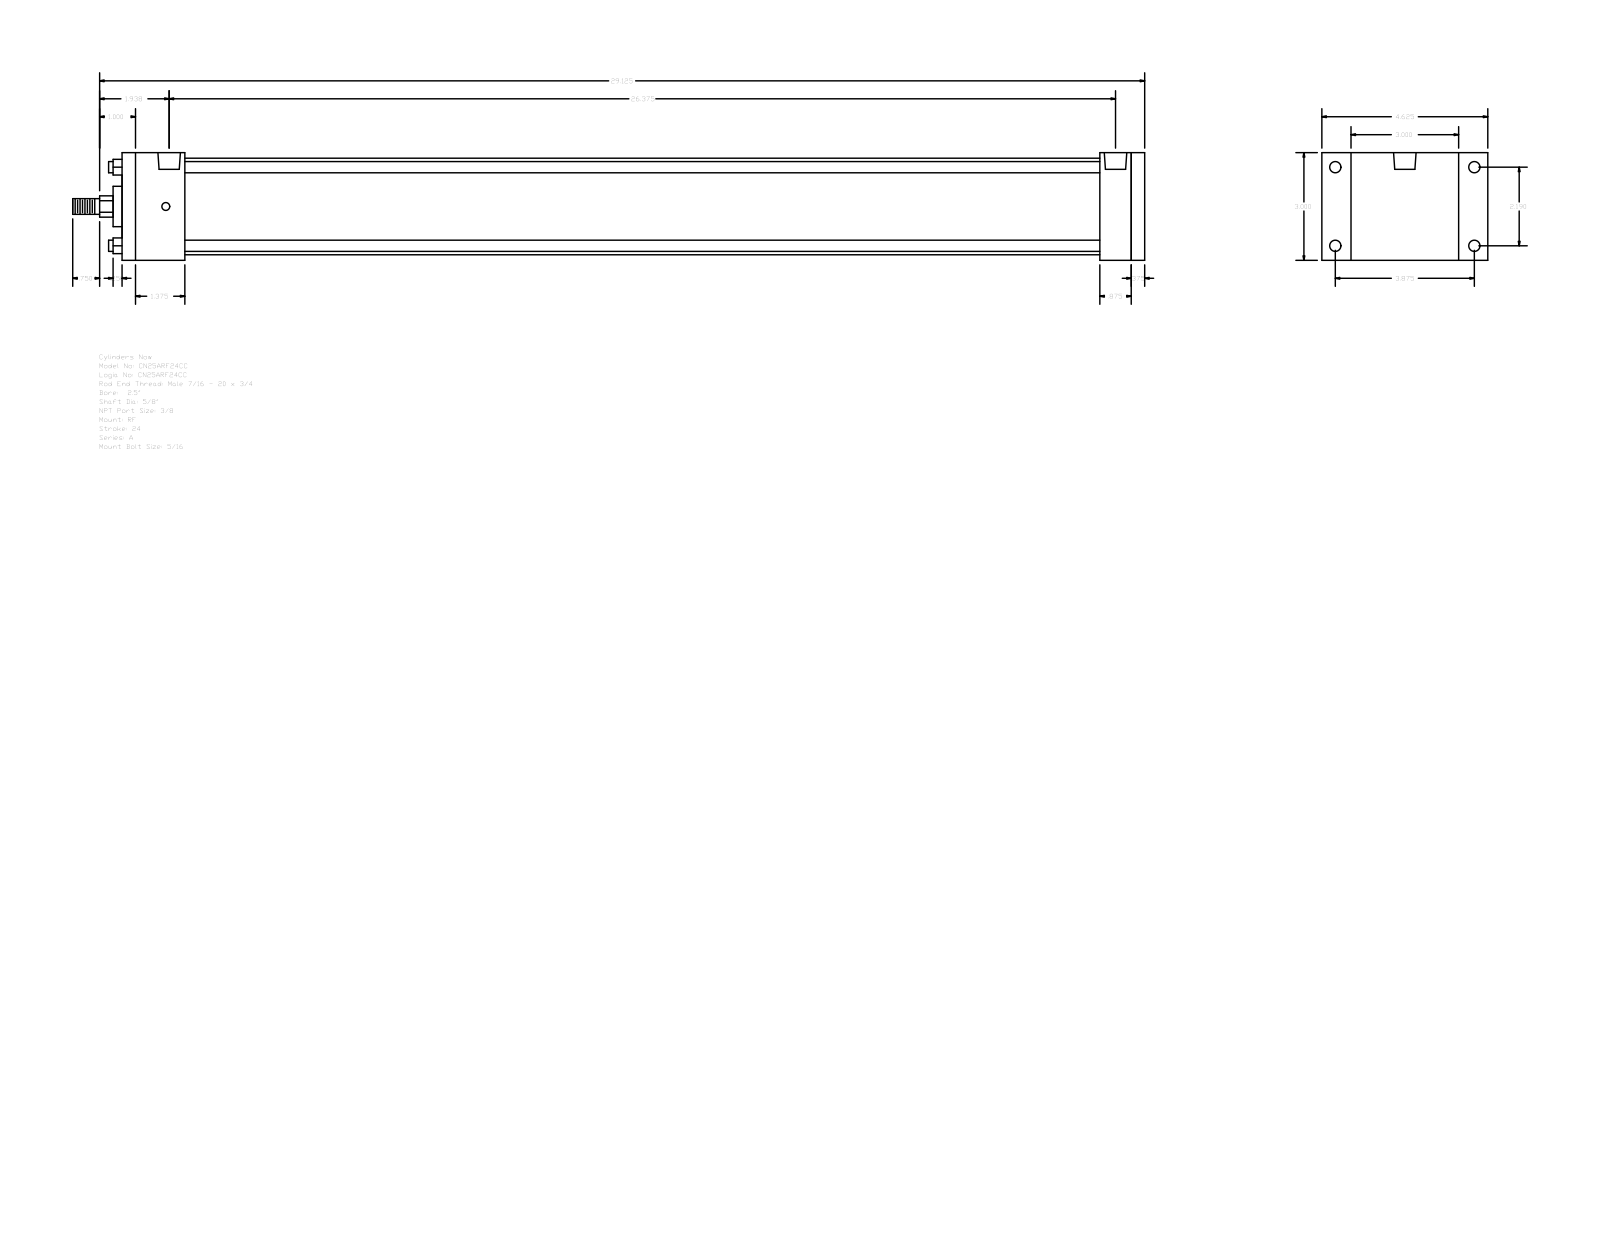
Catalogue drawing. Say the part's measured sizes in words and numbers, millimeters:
The part is named "A_RF__0250_0.625". Its 3-D file was written by "GSSL Pune (CONFIG_CONTROL_DESIGN)". It is 0 solids with 92 faces: 64 planar, 28 cylindrical and 0 other. Overall it measures 758.83 by 117.47 by 76.2 millimeters. Round holes: 4 of diameter 5.56, 4 of diameter 7.94, 2 of diameter 15.93. Round bosses or shafts: 4 of diameter 7.94, 1 of diameter 68.33, 1 of diameter 28.57, 1 of diameter 15.88, 1 of diameter 11.11. Partial cylindrical surfaces (rounded edges, fillets, slot ends): 1 of radius 7.54. The main face-to-face distances are 76.2, 723.89, 714.37, 9.52, 44.45, 31.75, 692.14, 647.69, 669.92, 679.44. The hole center spacings are 2.38, 55.62, 98.42, 113.05, 672.31, 674.69, 669.93.
